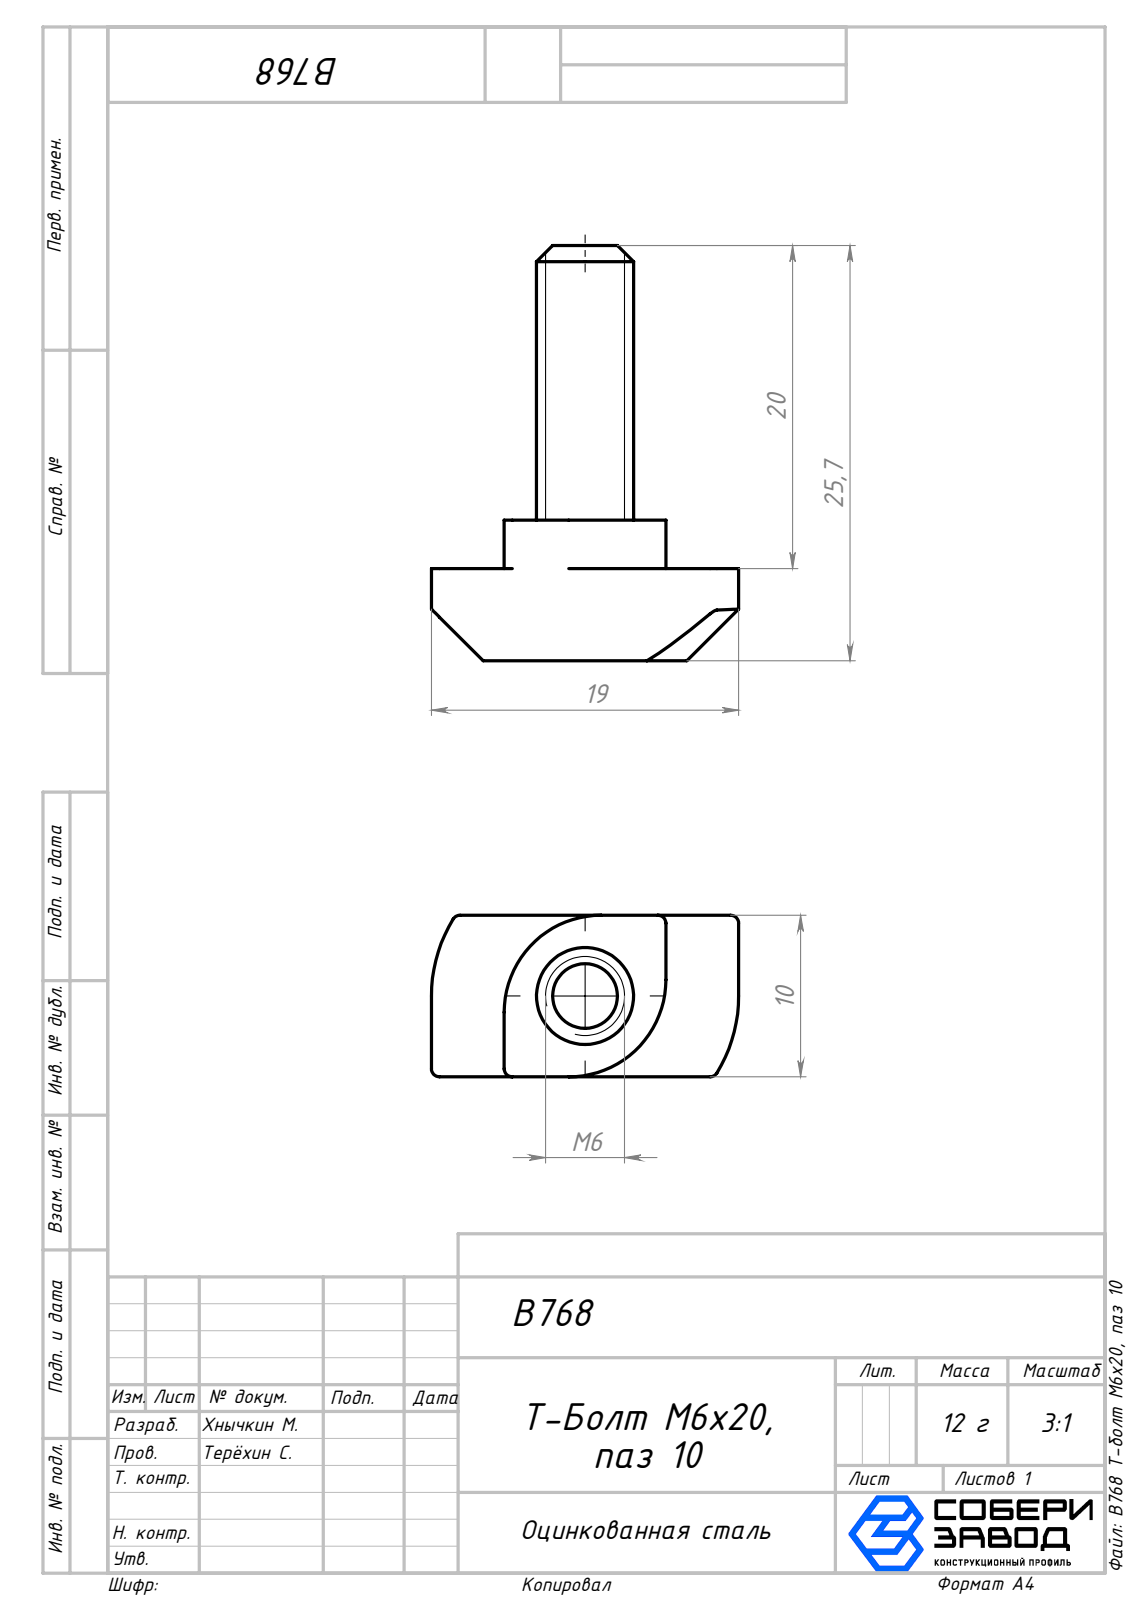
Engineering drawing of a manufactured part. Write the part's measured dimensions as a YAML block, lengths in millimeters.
part_name: "B768 Т-болт М6х20, паз 10"
step_written_by: "SolidWorks 2025 (AUTOMOTIVE_DESIGN)"
units: millimeters
bodies: {solids: 1, faces: 29, planar: 13, cylindrical: 12, other: 4}
overall_size: [25.7, 19, 10]
volume: 1675
surface_area: 1036
round_bosses_or_shafts:
  - {diameter: 6, count: 1}
partial_cylinders:
  - {radius: 0.5, count: 6}
  - {radius: 6, count: 2}
  - {radius: 9.08, count: 2}
face_to_face_distances: [10, 5.7, 8.7, 3, 4.5, 14.5, 25.7, 20, 17, 19]
